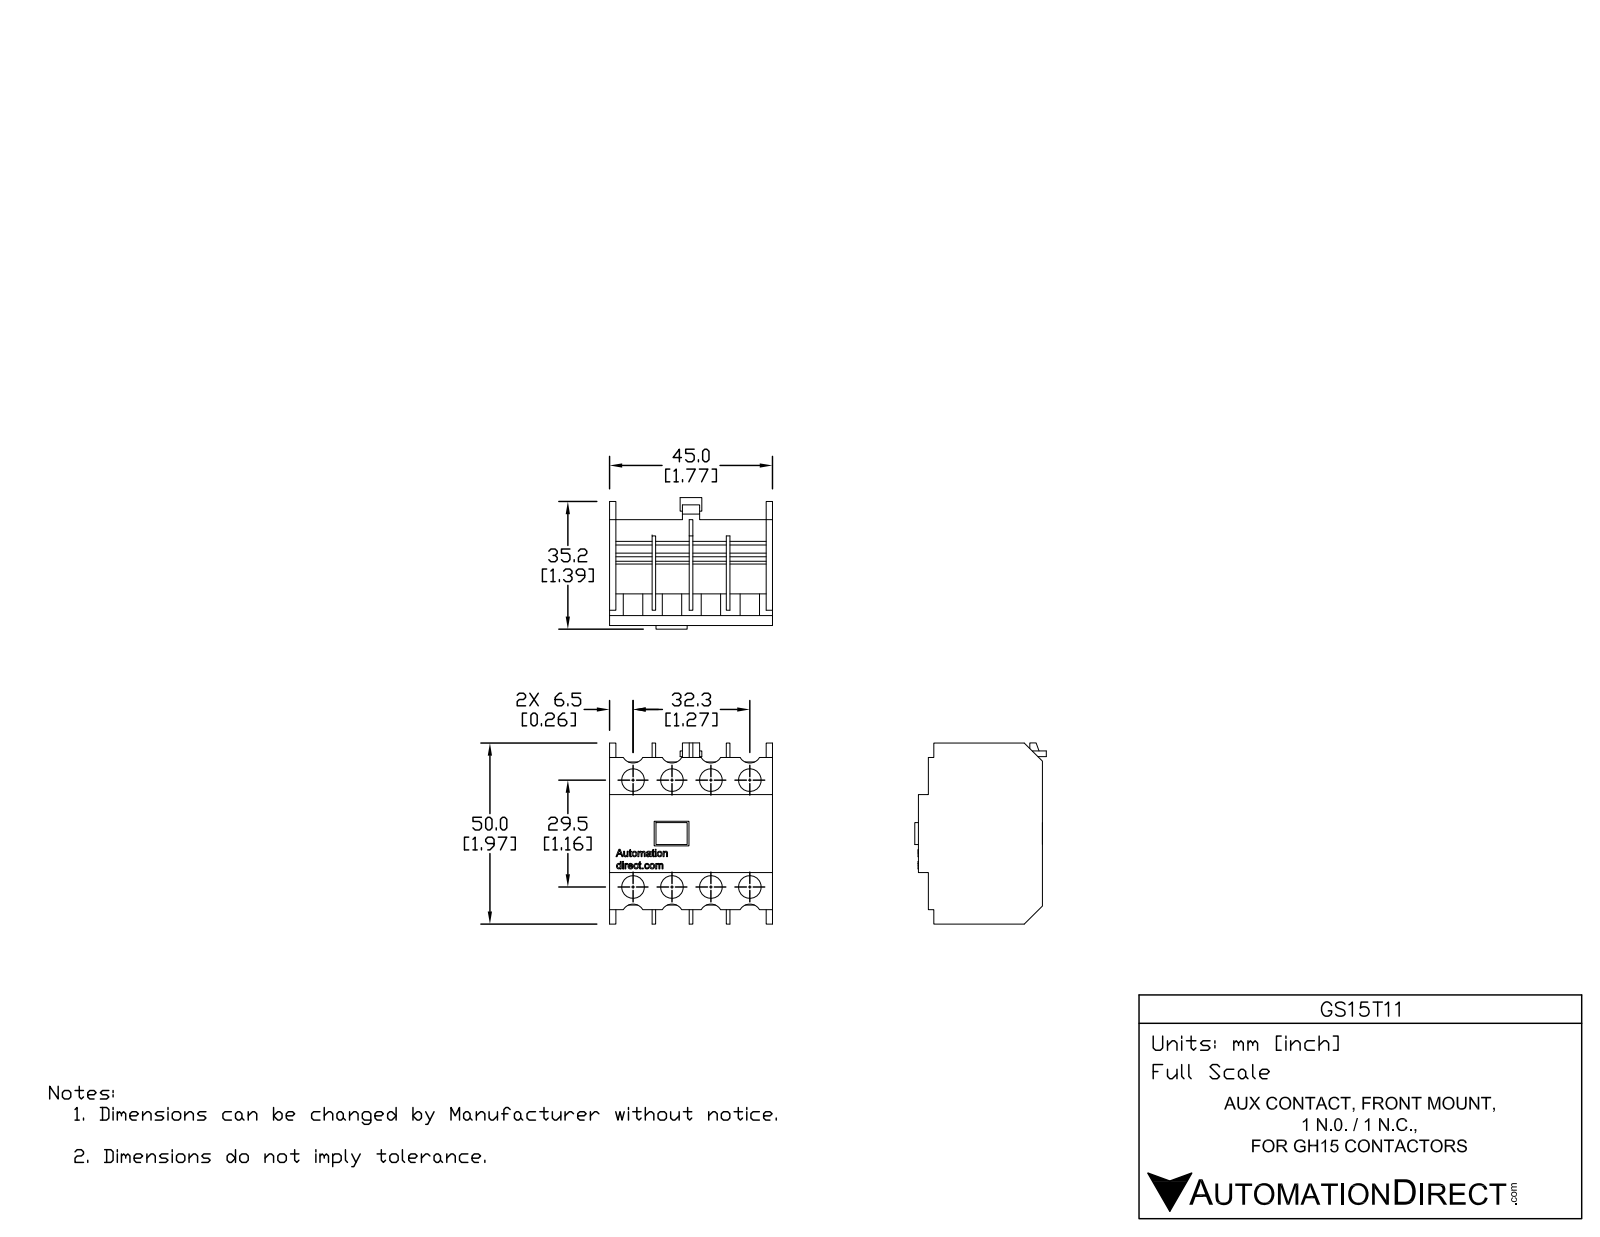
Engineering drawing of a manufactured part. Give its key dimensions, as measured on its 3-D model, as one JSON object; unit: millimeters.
{"part_name": "GH15T11", "step_written_by": "SolidWorks 2009 (CONFIG_CONTROL_DESIGN)", "units": "millimeters", "bodies": {"solids": 1, "faces": 509, "planar": 359, "cylindrical": 24, "other": 126}, "overall_size": [50.03, 45, 36.32], "volume_mm3": 38863, "surface_area_mm2": 16844, "round_holes": [[6.25, 8]], "partial_cylinders_radius": [[3.12, 8]], "face_to_face_distances": [10.25, 20.5, 45, 1.75, 43.25, 1, 6, 22, 14.25, 12.75], "hole_center_spacings": [10.75, 31.4, 21.5, 29.5, 36.5, 32.25, 43.71]}
